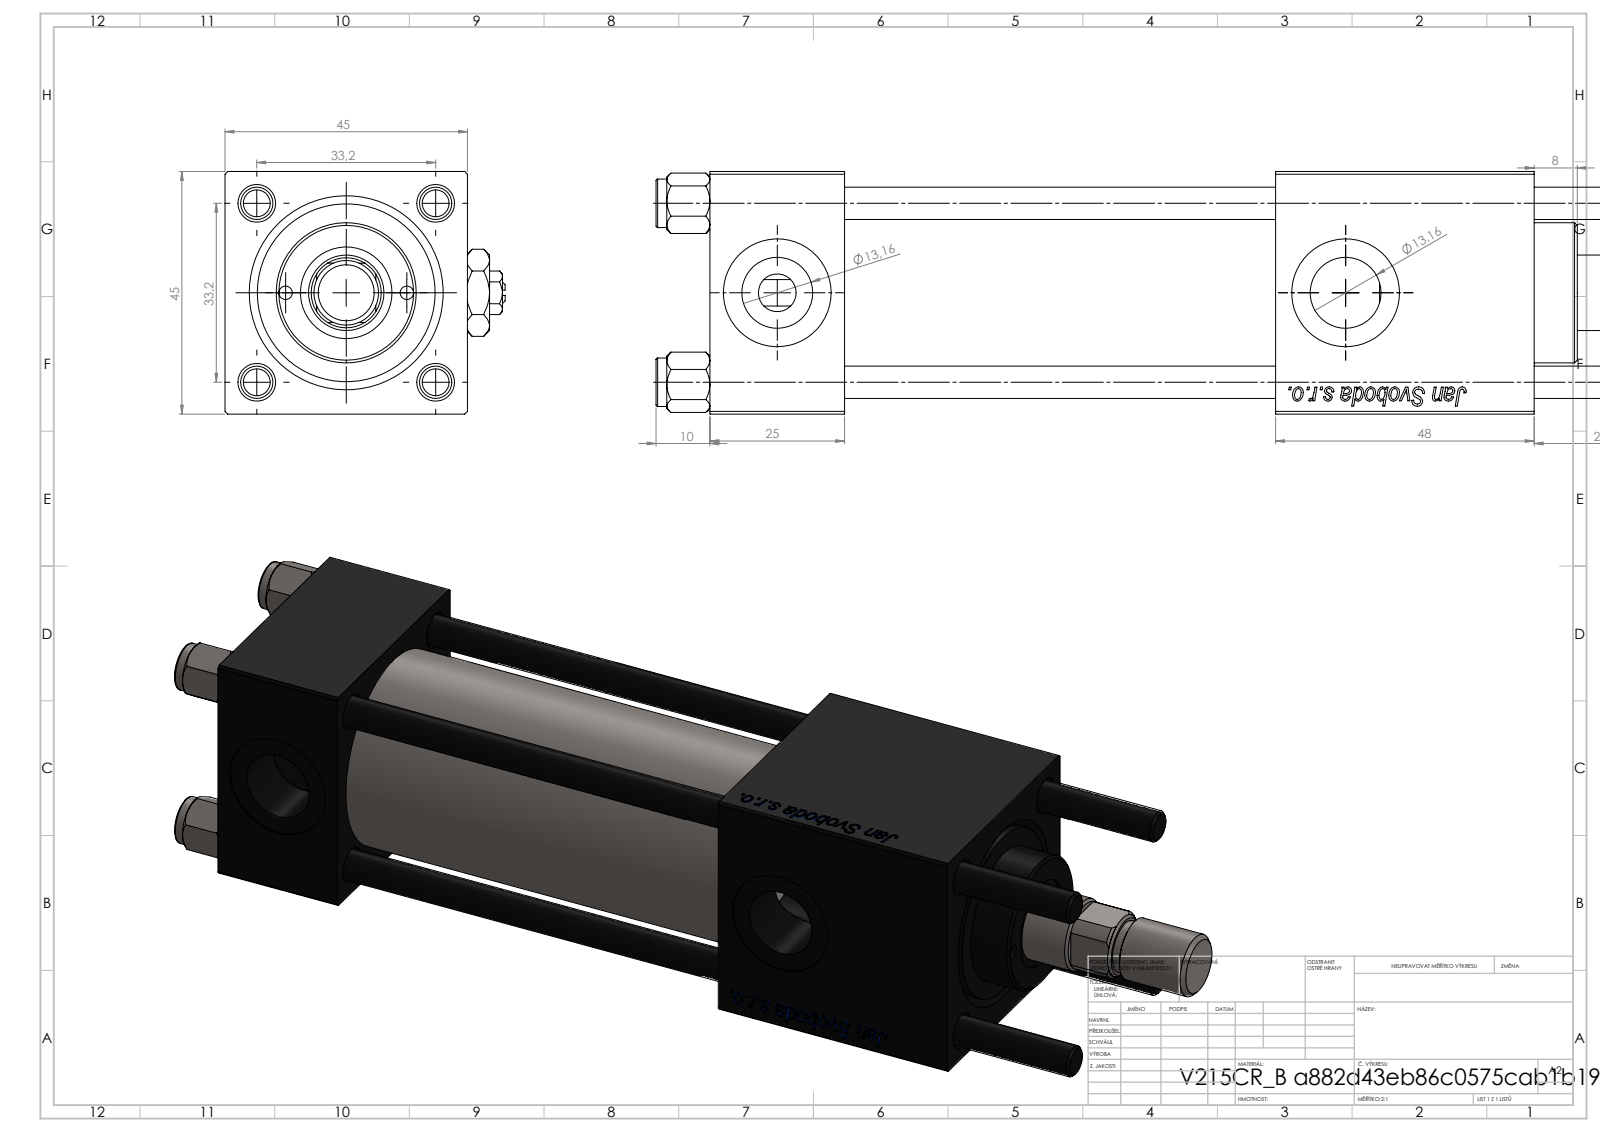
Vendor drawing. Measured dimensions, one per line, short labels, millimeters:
name: V215CR_B-1; V215_VC_A; V215CR_VCP_B; V215CR_B_TYCINKA (+3 more)
written by: SolidWorks 2019 (CONFIG_CONTROL_DESIGN)
unit: mm
bodies: 13 solids, 1228 faces (460 planar, 92 cylindrical, 676 other)
size: 204 × 52 × 45
volume: 217 028 mm³; area: 84 883 mm²
holes: 4× ⌀6, 2× ⌀2.5, 2× ⌀7, 2× ⌀13.16, 2× ⌀20, 1× ⌀6.5, 1× ⌀14, 1× ⌀17, 1× ⌀24, 1× ⌀32, 1× ⌀33
bosses: 4× ⌀9, 1× ⌀38, 1× ⌀26, 1× ⌀12, 1× ⌀10
rounds: 1× R6.5
face distances: 45, 25, 153, 128, 105, 80, 48, 124.3, 99.3, 19.3
hole spacings: 17.44, 23.48, 32.42, 33.2, 11.25, 46.95, 22.5, 105.5
